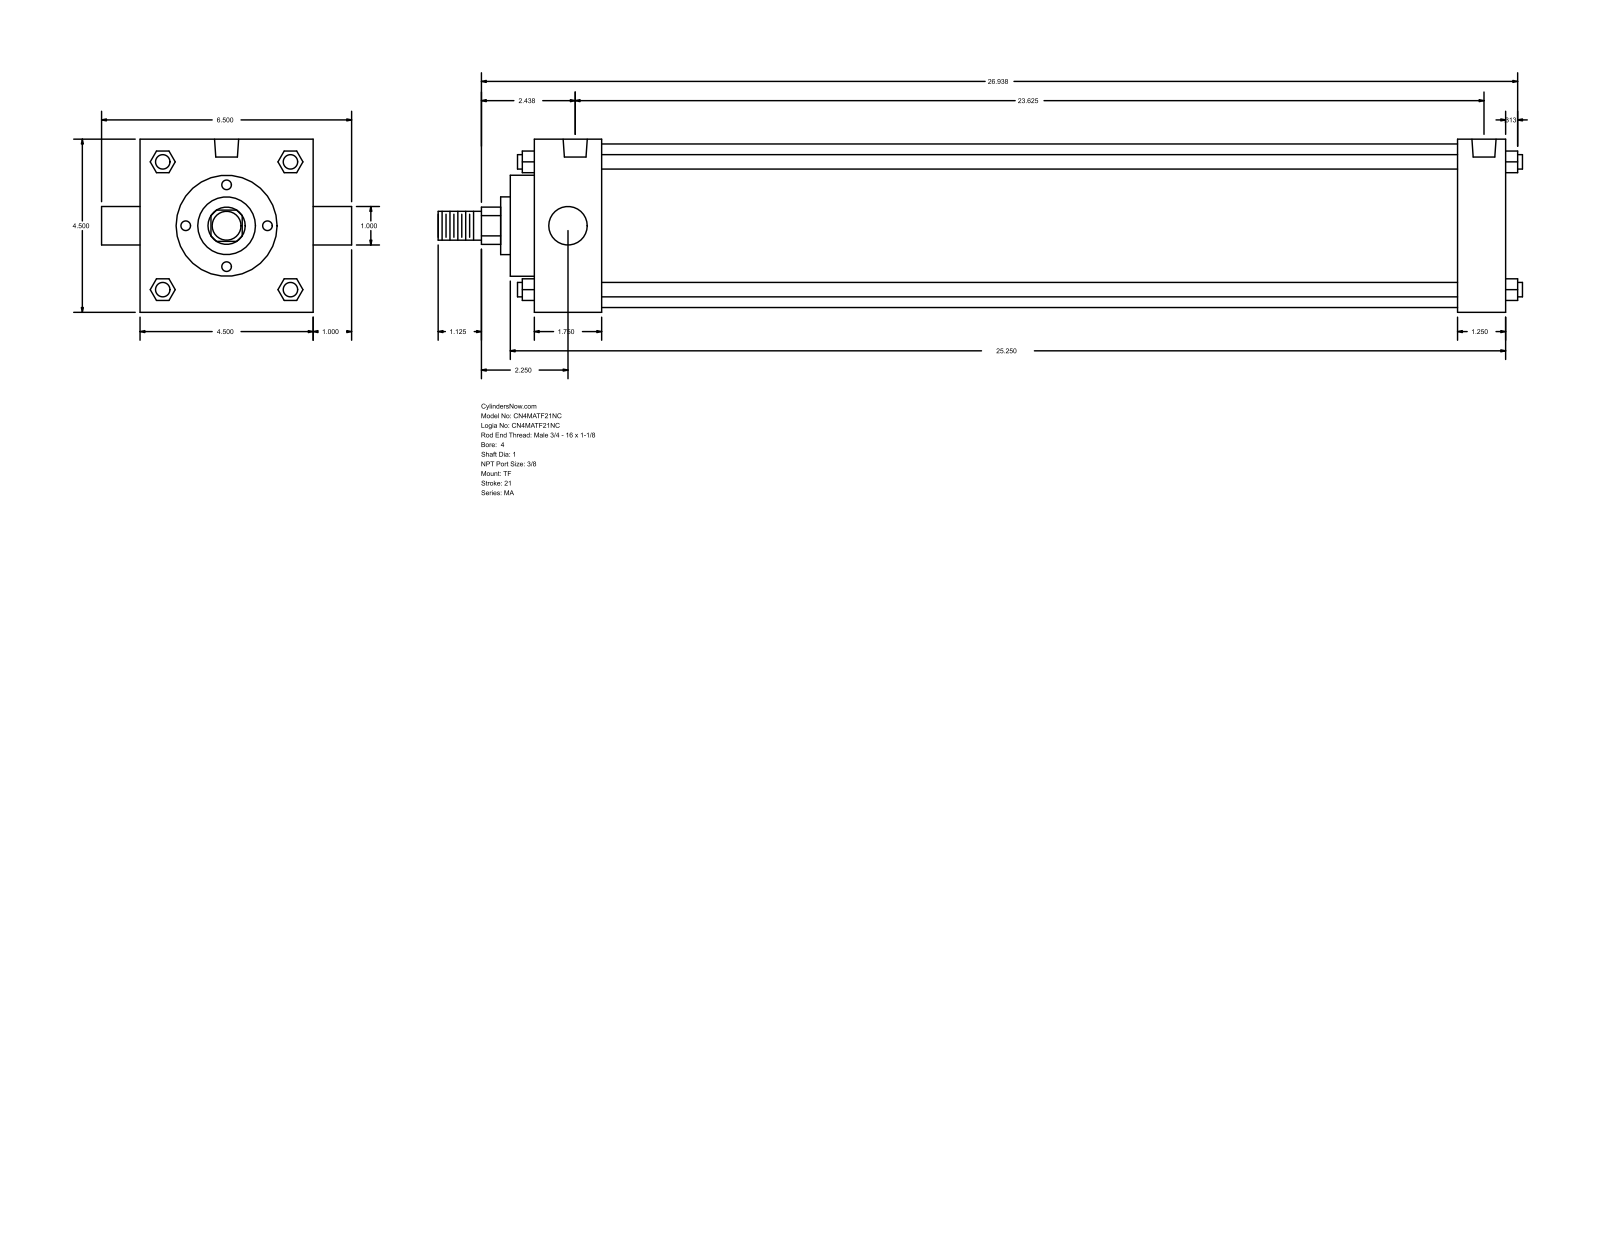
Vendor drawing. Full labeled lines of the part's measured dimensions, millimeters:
Part name (STEP PRODUCT): MA_TF__0400_1
STEP written by: GSSL Pune (CONFIG_CONTROL_DESIGN)
Units: millimetres
Bodies: 0 solids, 122 faces (93 planar, 29 cylindrical, 0 other)
Overall size (bounding box): 715.96 × 165.1 × 114.3
Round holes (diameter × count): ⌀11.11 ×3, ⌀15.93 ×2
Round bosses / shafts (diameter × count): ⌀9.53 ×4, ⌀25.4 ×2, ⌀107.95 ×1, ⌀66.67 ×1, ⌀38.1 ×1, ⌀19.05 ×1
Partial cylindrical surfaces — rounded edges, fillets, slot ends (radius × count): R12.29 ×1
Main face-to-face distances: 114.3, 641.35, 609.6, 31.75, 44.46, 565.14, 596.89, 657.22, 15.87, 60.33
Hole centre spacings: 4.76, 595.32, 590.56, 600.08
